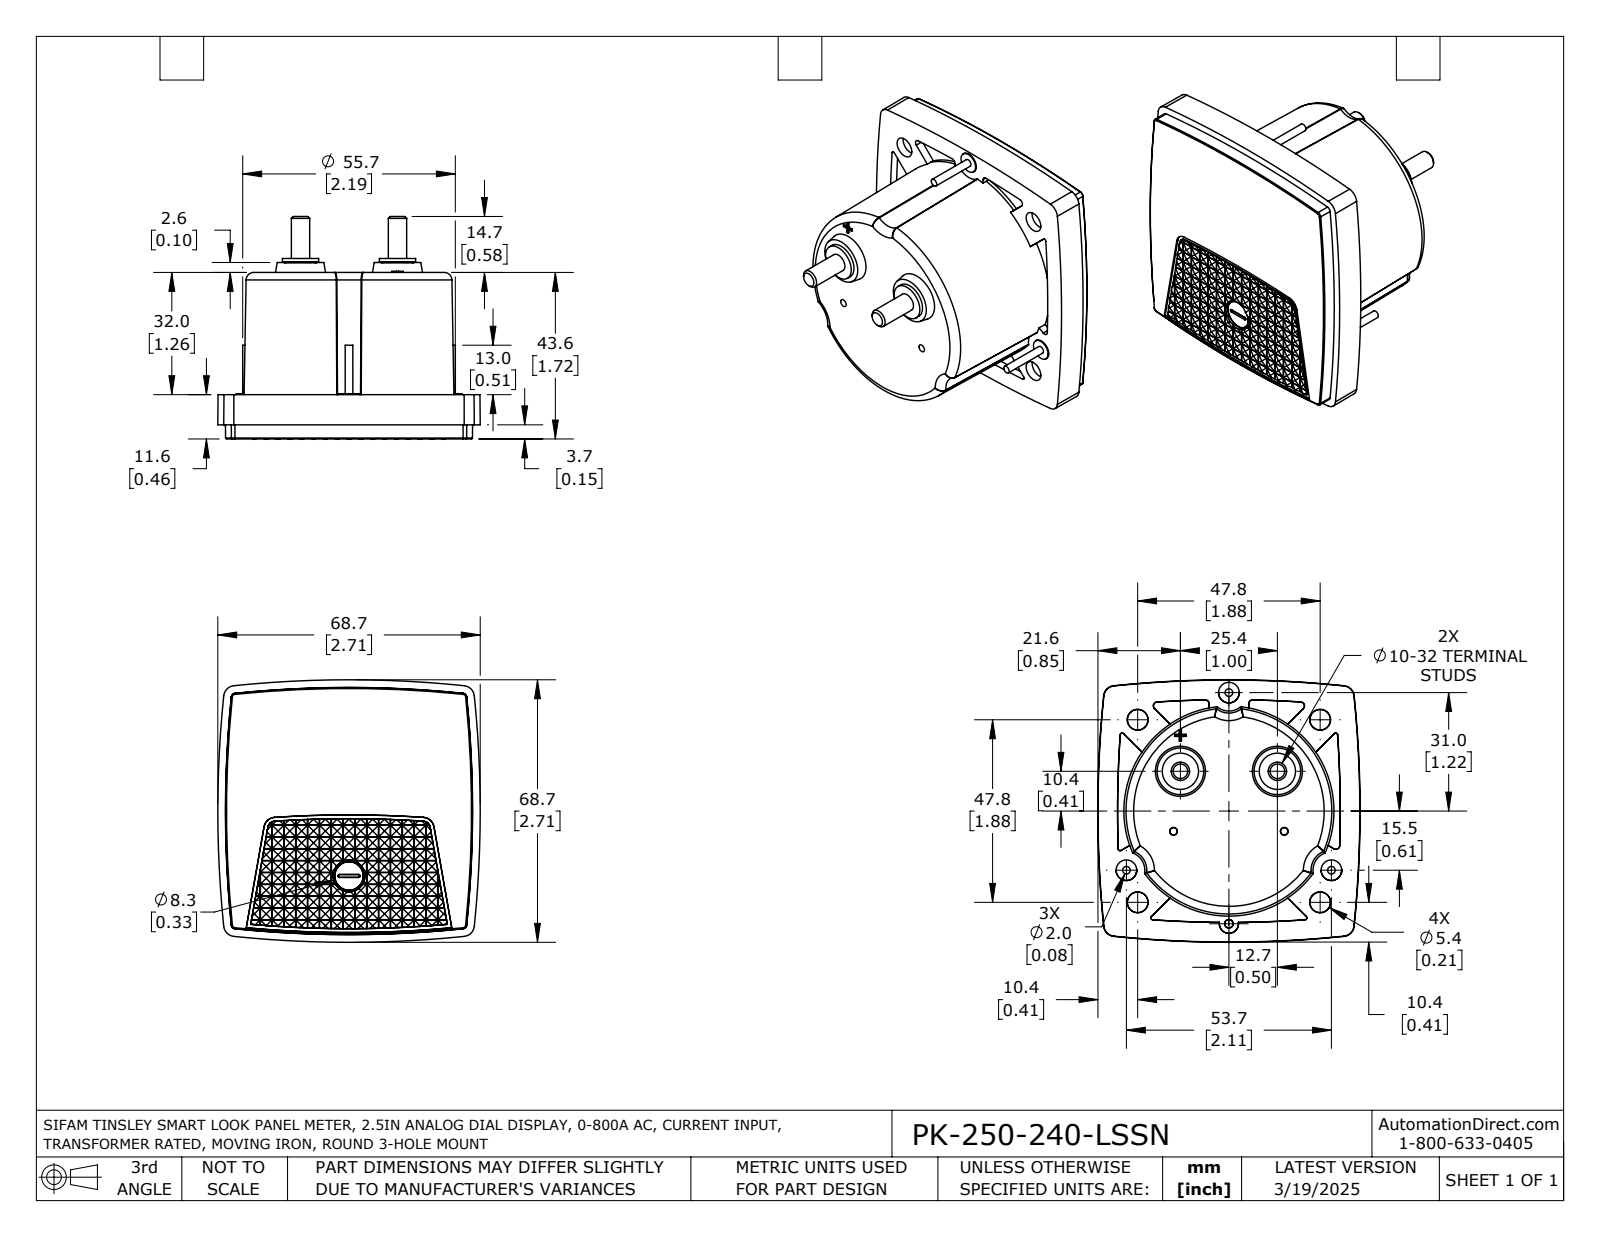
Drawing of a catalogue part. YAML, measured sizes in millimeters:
part_name: "PK-250-240-LSSN"
step_written_by: "SolidWorks 2021 (AUTOMOTIVE_DESIGN)"
units: millimeters
bodies: {solids: 1, faces: 1550, planar: 1165, cylindrical: 265, other: 120}
overall_size: [68.7, 68.7, 58.3]
volume: 124400
surface_area: 19620
round_bosses_or_shafts:
  - {diameter: 5.4, count: 3}
  - {diameter: 2, count: 3}
  - {diameter: 9.5, count: 2}
  - {diameter: 4.8, count: 2}
  - {diameter: 5.5, count: 1}
partial_cylinders:
  - {radius: 4.2, count: 2}
  - {radius: 27.5, count: 1}
face_to_face_distances: [43.6, 32, 11.6, 0.6, 2.2, 2.4, 7.9, 3, 1.8, 34.2]
